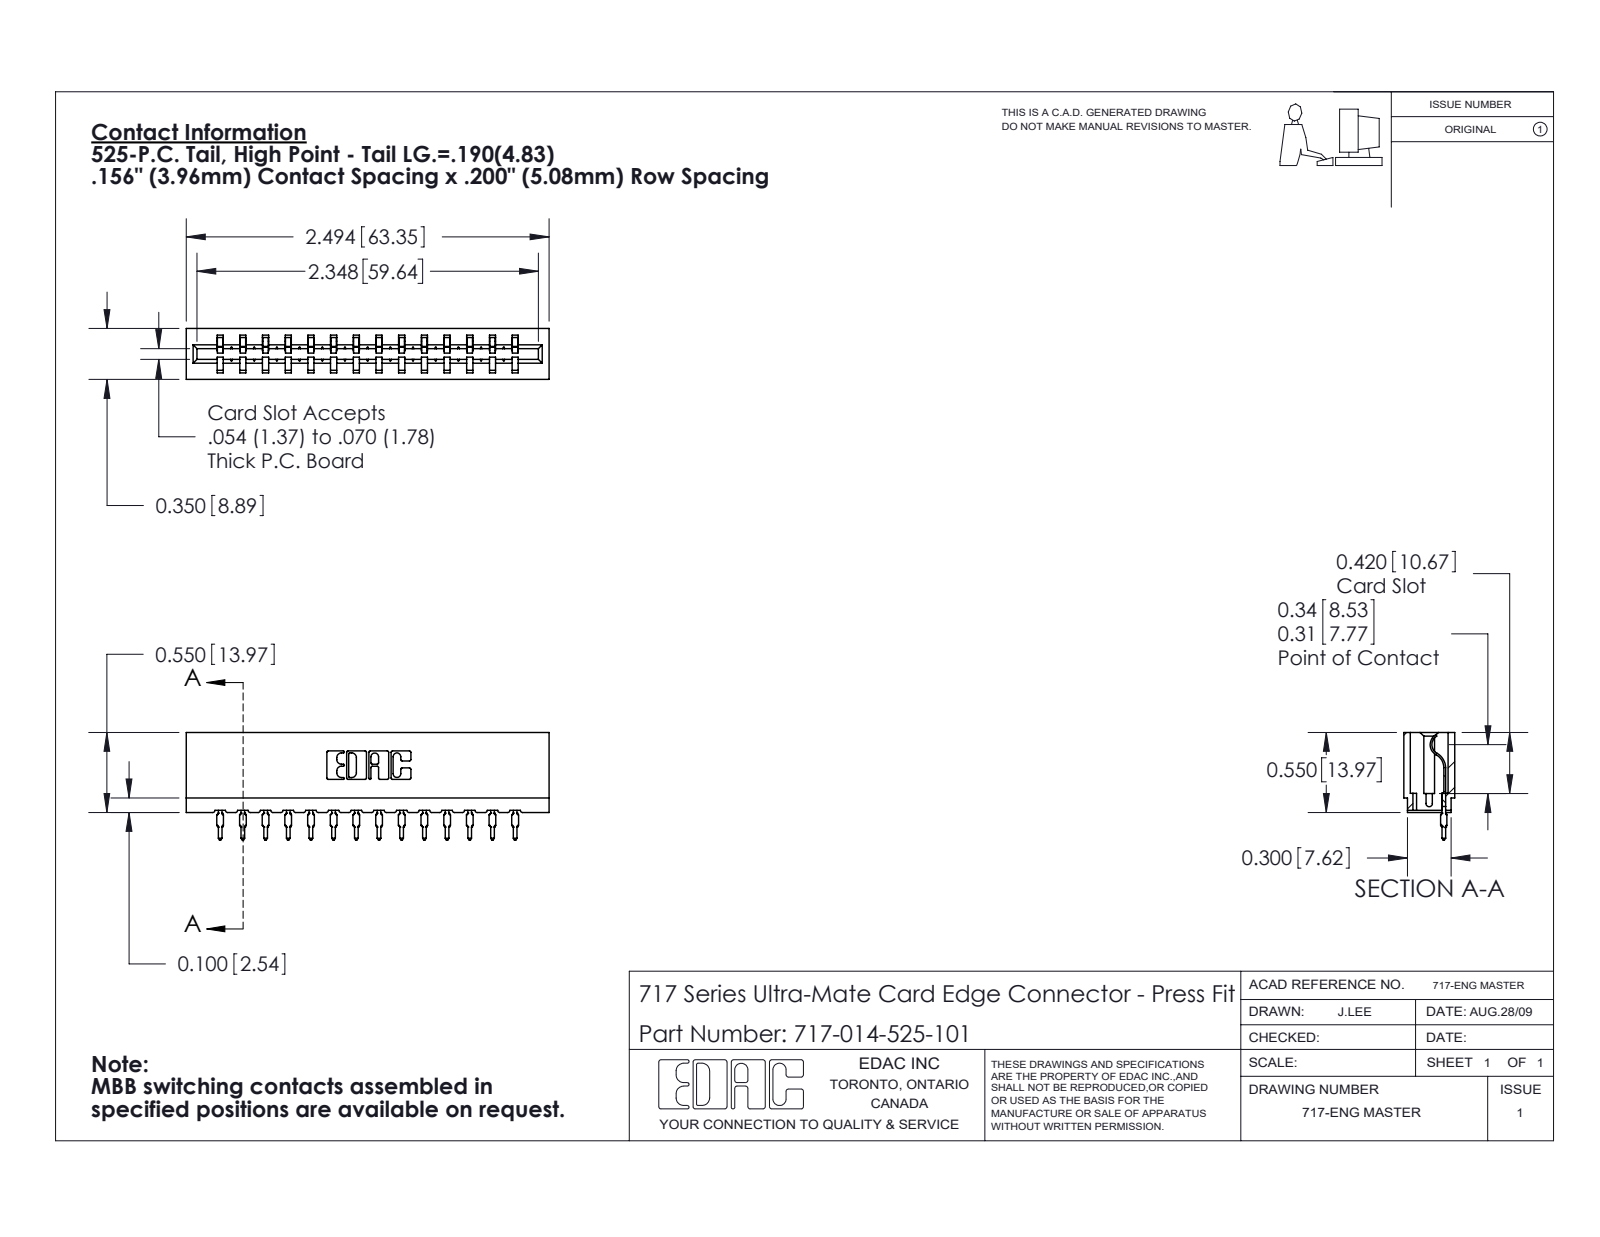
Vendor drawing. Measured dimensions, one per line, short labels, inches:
name: 745-292-001_525; 717 Part_Insulator Option - 06; 717-014-525-101
written by: SolidWorks 2020 (CONFIG_CONTROL_DESIGN)
unit: in
bodies: 15 solids, 1676 faces (1006 planar, 306 cylindrical, 364 other)
size: 2.494 × 0.739 × 0.35
volume: 0.333 in³; area: 11.36 in²
rounds: 28× R0.015, 28× R0.021, 22× R0.01, 6× R0.007, 6× R0.031, 4× R0.005, 4× R0.011, 3× R0.026
face distances: 0.212, 0.138, 0.156, 0.35, 0.624, 0.198, 0.312, 0.468, 0.074, 0.354
